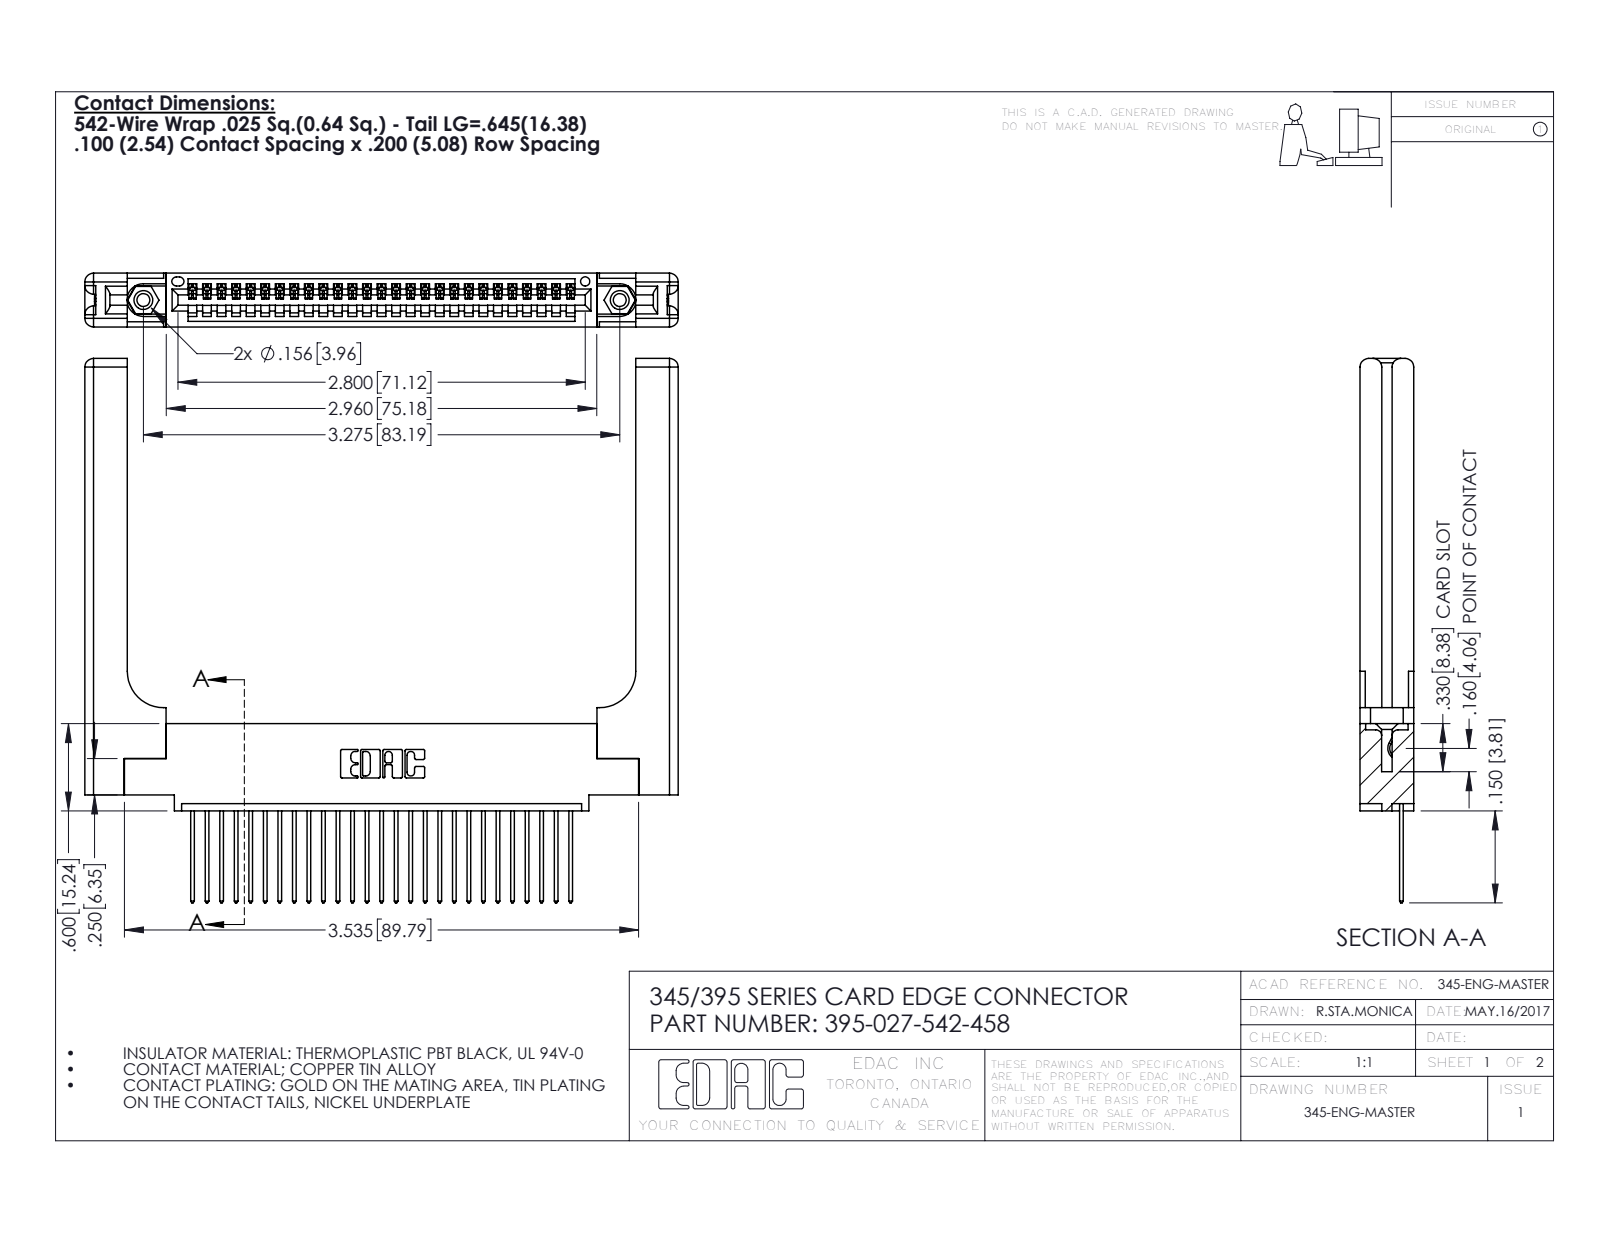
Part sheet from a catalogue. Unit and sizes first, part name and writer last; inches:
Units: inches
Overall size (bounding box): 4.079 × 3.742 × 0.37
Round holes (diameter × count): ⌀0.089 ×2, ⌀0.125 ×2, ⌀0.156 ×2, ⌀0.064 ×1
Round bosses / shafts (diameter × count): ⌀0.155 ×2
Partial cylindrical surfaces — rounded edges, fillets, slot ends (radius × count): R0.006 ×54, R0.01 ×54, R0.01 ×22, R0.06 ×16, R0.007 ×6, R0.031 ×6, R0.026 ×3, R0.03 ×2
Main face-to-face distances: 0.37, 0.072, 0.298, 0.098, 0.272, 0.025, 0.2, 0.148, 0.15, 0.077
Hole centre spacings: 0.27, 3.04, 3.275
Volume: 1.111 in³ · Surface area: 28.61 in²
Bodies: 32 solids, 1952 faces (1312 planar, 580 cylindrical, 60 other)
Part name (STEP PRODUCT): 345-292-001_345-293-142; 345 Part_0.110 Offset - 0.156 Dia-TH; 345-220-058_345-220-058; 345-250-001_345-250-001-102 (+1 more)
STEP written by: SolidWorks 2016 (CONFIG_CONTROL_DESIGN)
